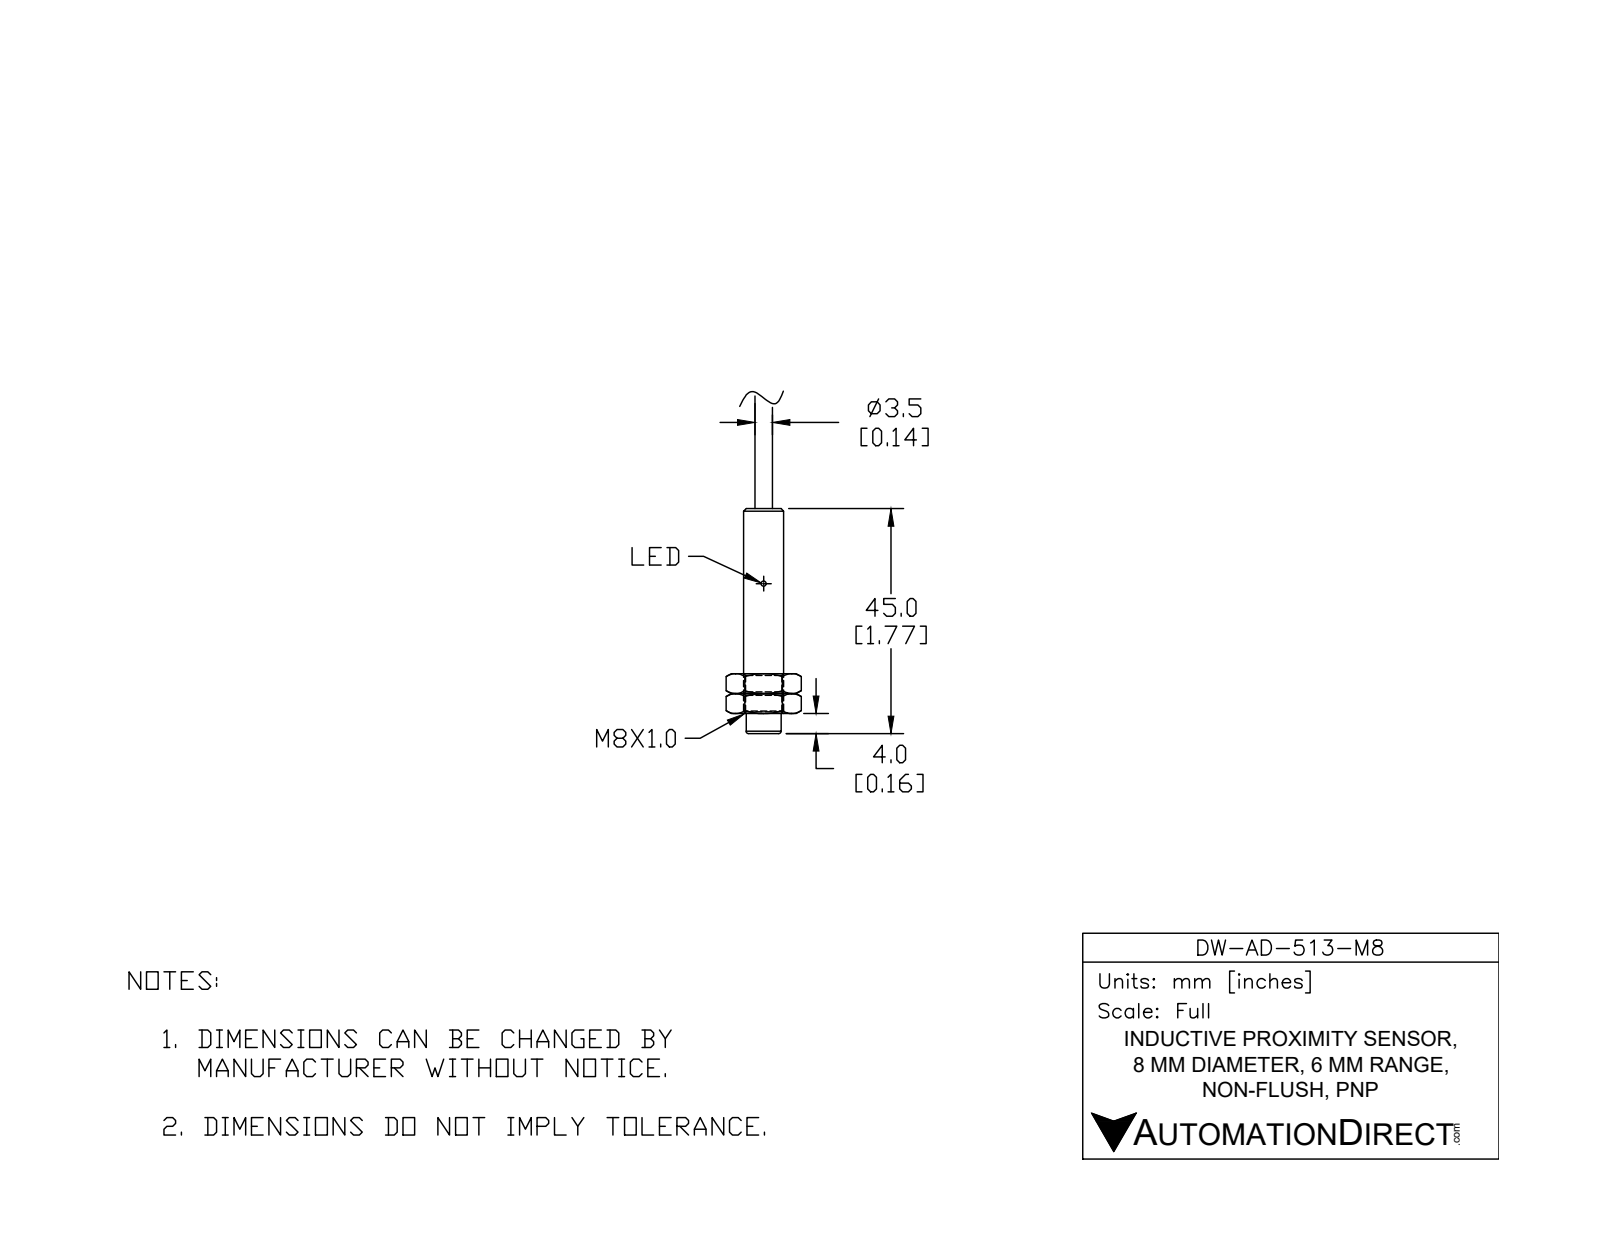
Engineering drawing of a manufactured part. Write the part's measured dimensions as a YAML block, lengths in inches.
part_name: "DW-AD-513-M8"
step_written_by: "SolidWorks 2017 (AUTOMOTIVE_DESIGN)"
units: inches
bodies: {solids: 2, faces: 14, planar: 6, cylindrical: 4, other: 4}
overall_size: [2.803, 0.315, 0.315]
volume: 0.166
surface_area: 2.617
round_bosses_or_shafts:
  - {diameter: 0.315, count: 1}
  - {diameter: 0.272, count: 1}
  - {diameter: 0.256, count: 1}
  - {diameter: 0.197, count: 1}
face_to_face_distances: [0.165, 2.803, 2.638, 1.791, 1.626, 1.012, 1.772, 1.606, 0.02, 1.031]
